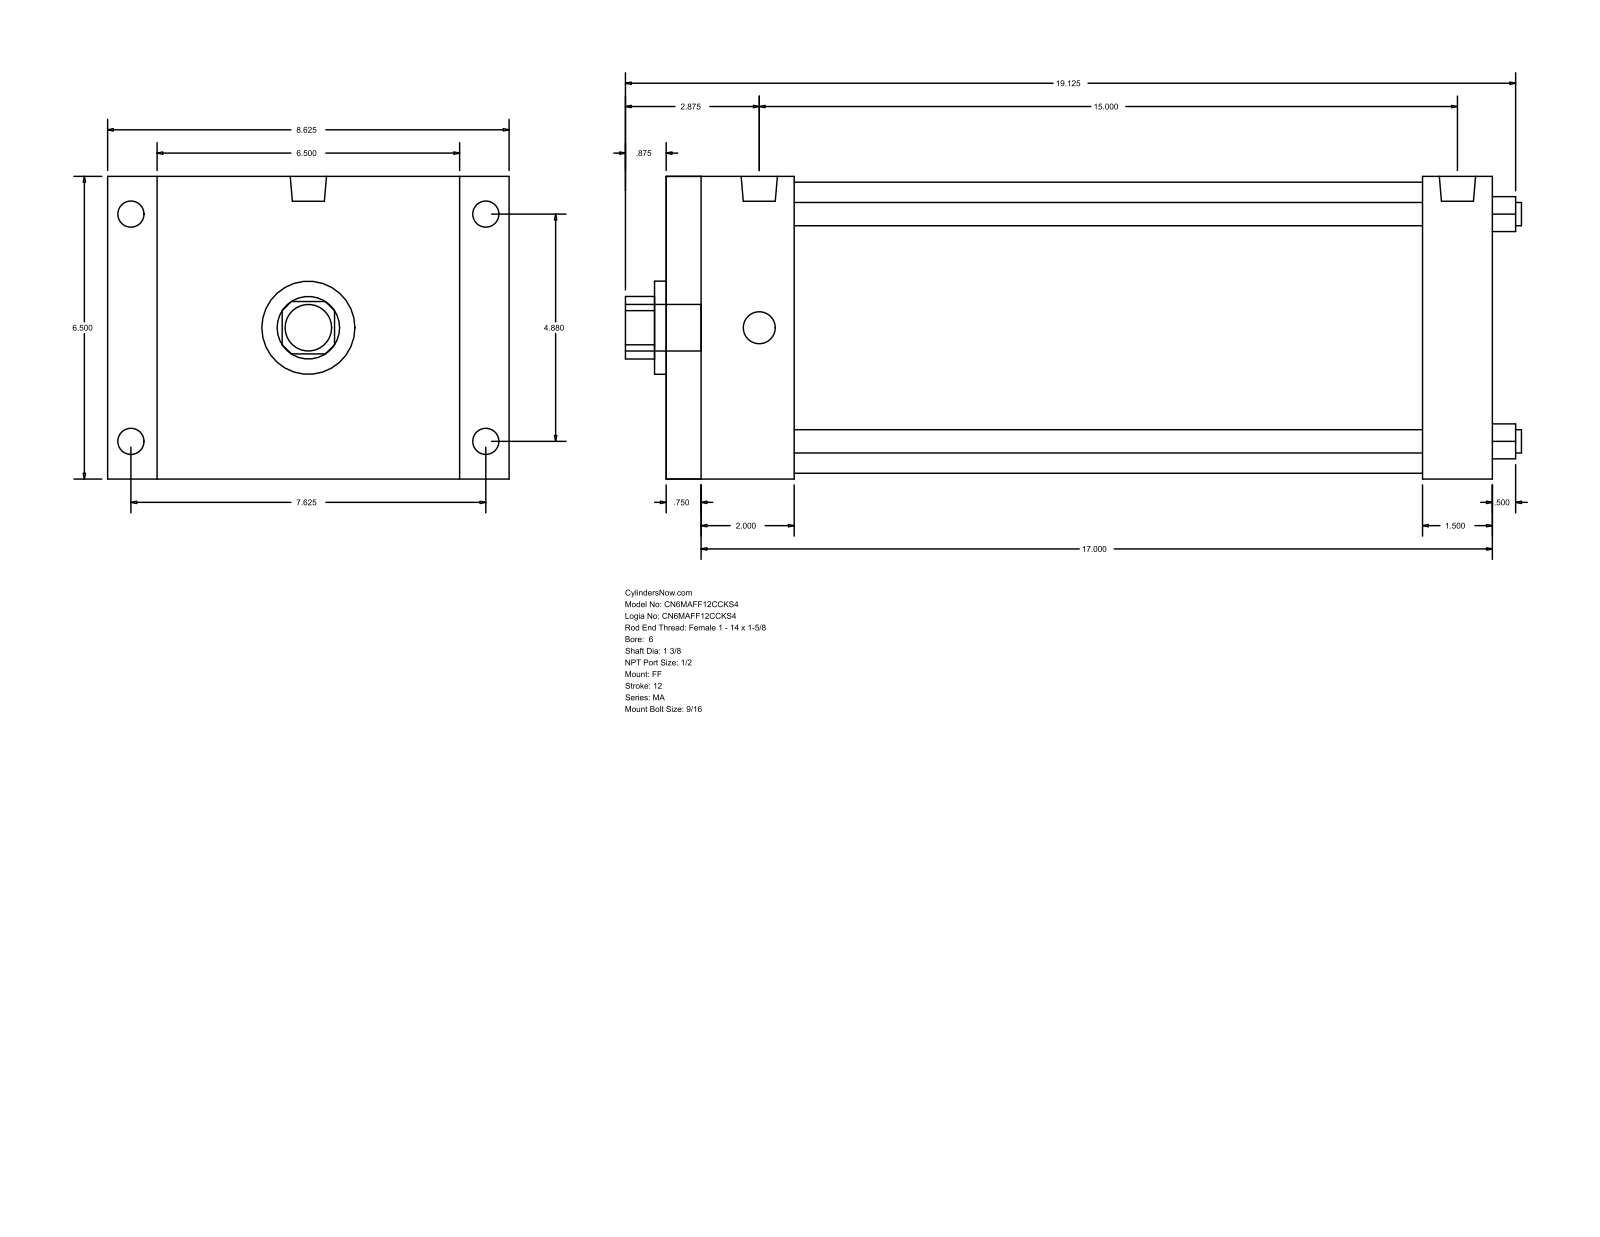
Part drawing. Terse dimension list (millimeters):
name: MA_FF__0600_1.375
written by: GSSL Pune (CONFIG_CONTROL_DESIGN)
unit: mm
bodies: 0 solids, 92 faces (64 planar, 28 cylindrical, 0 other)
size: 488.95 × 219.07 × 165.1
holes: 4× ⌀12.7, 1× ⌀34.92, 1× ⌀50.8, 1× ⌀158.75
bosses: 4× ⌀17.46, 4× ⌀14.29, 2× ⌀19.77, 1× ⌀25.4
rounds: 1× R17.06
face distances: 165.1, 450.84, 15.87, 434.97, 66.67, 50.8, 384.17, 412.75, 396.88, 346.08
hole spacings: 87.65, 123.96, 175.31
